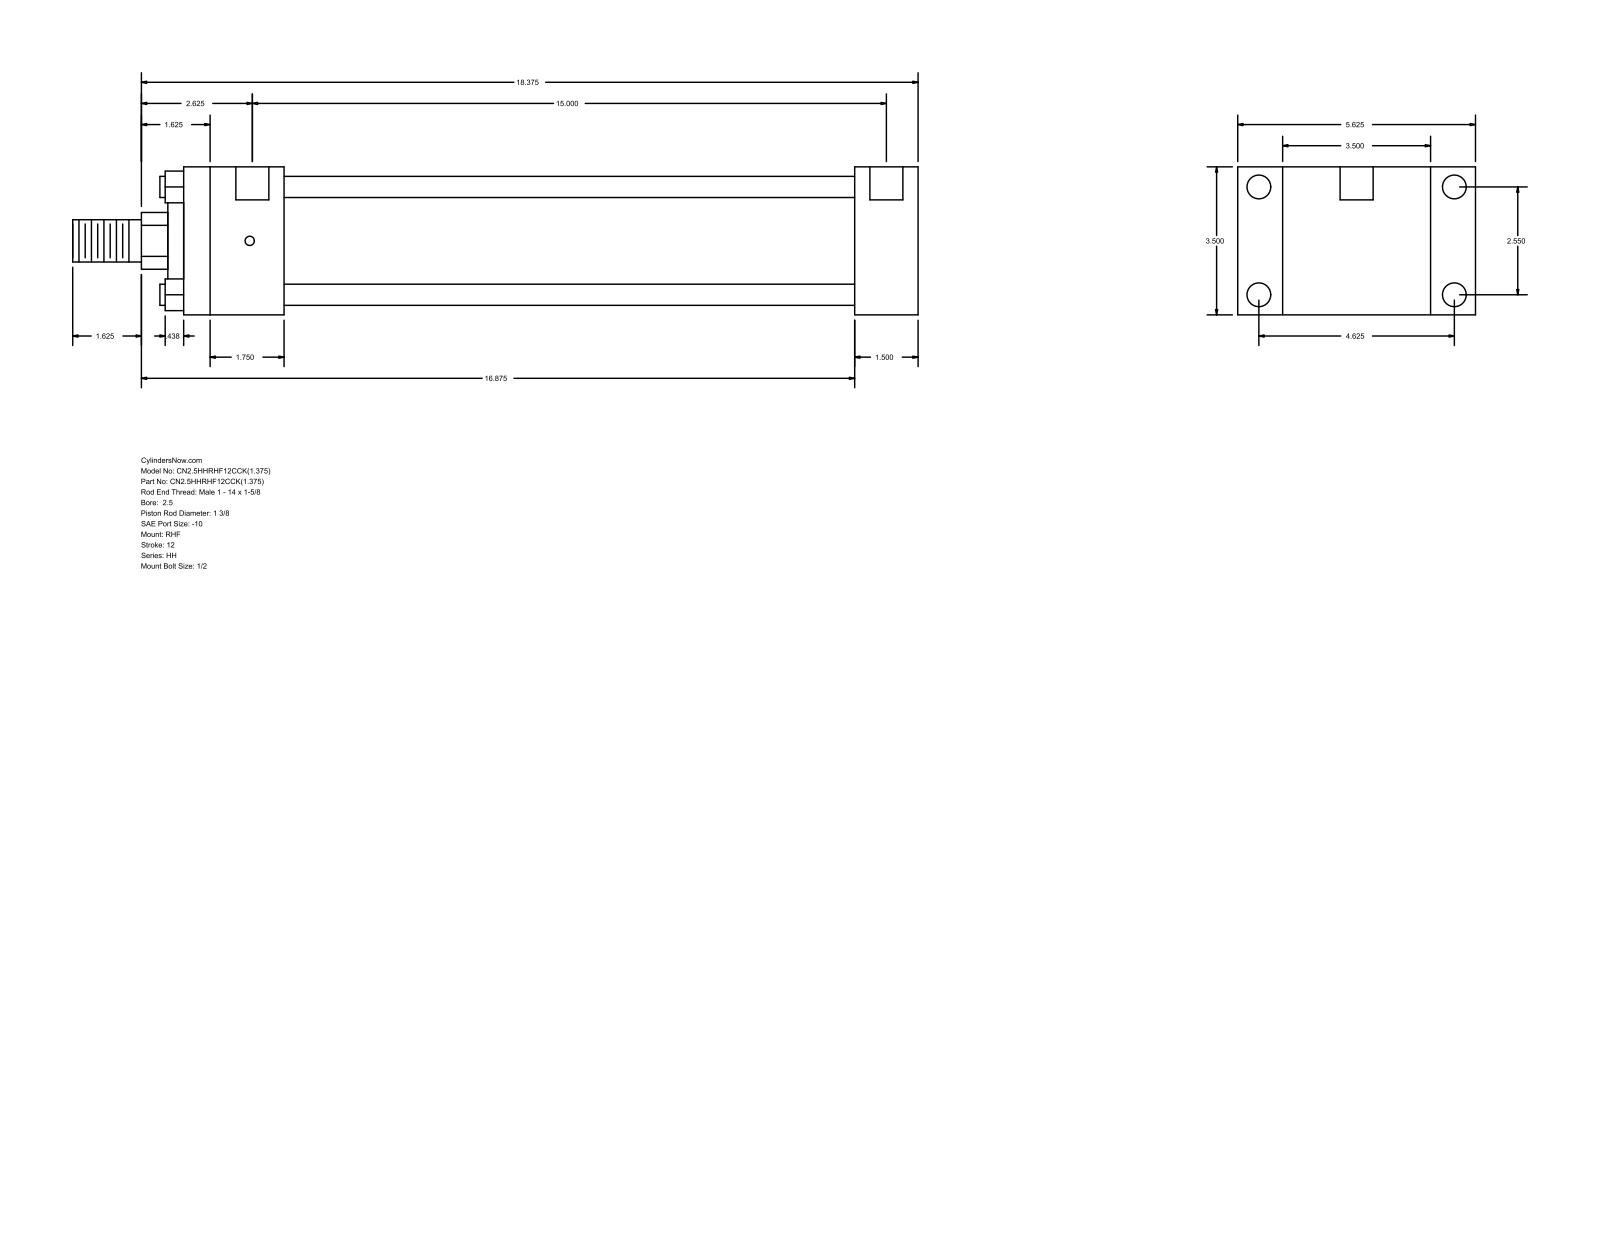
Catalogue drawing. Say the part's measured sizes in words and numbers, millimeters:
The part is named "HH_RHF__0250_1.375". Its 3-D file was written by "GSSL Pune (CONFIG_CONTROL_DESIGN)". It is 0 solids with 88 faces: 60 planar, 28 cylindrical and 0 other. Overall it measures 508 by 142.88 by 88.9 millimeters. Round holes: 4 of diameter 5.56, 4 of diameter 14.3, 2 of diameter 19.84. Round bosses or shafts: 4 of diameter 12.7, 1 of diameter 73.03, 1 of diameter 50.8, 1 of diameter 34.92, 1 of diameter 25.4. Partial cylindrical surfaces (rounded edges, fillets, slot ends): 1 of radius 17.06. The main face-to-face distances are 88.9, 38.11, 26.99, 115.89, 403.22, 441.33, 142.88, 60.32, 342.9, 381.01. The hole center spacings are 1.58, 64.76, 117.48, 134.15, 382.59, 384.17, 381.01.
